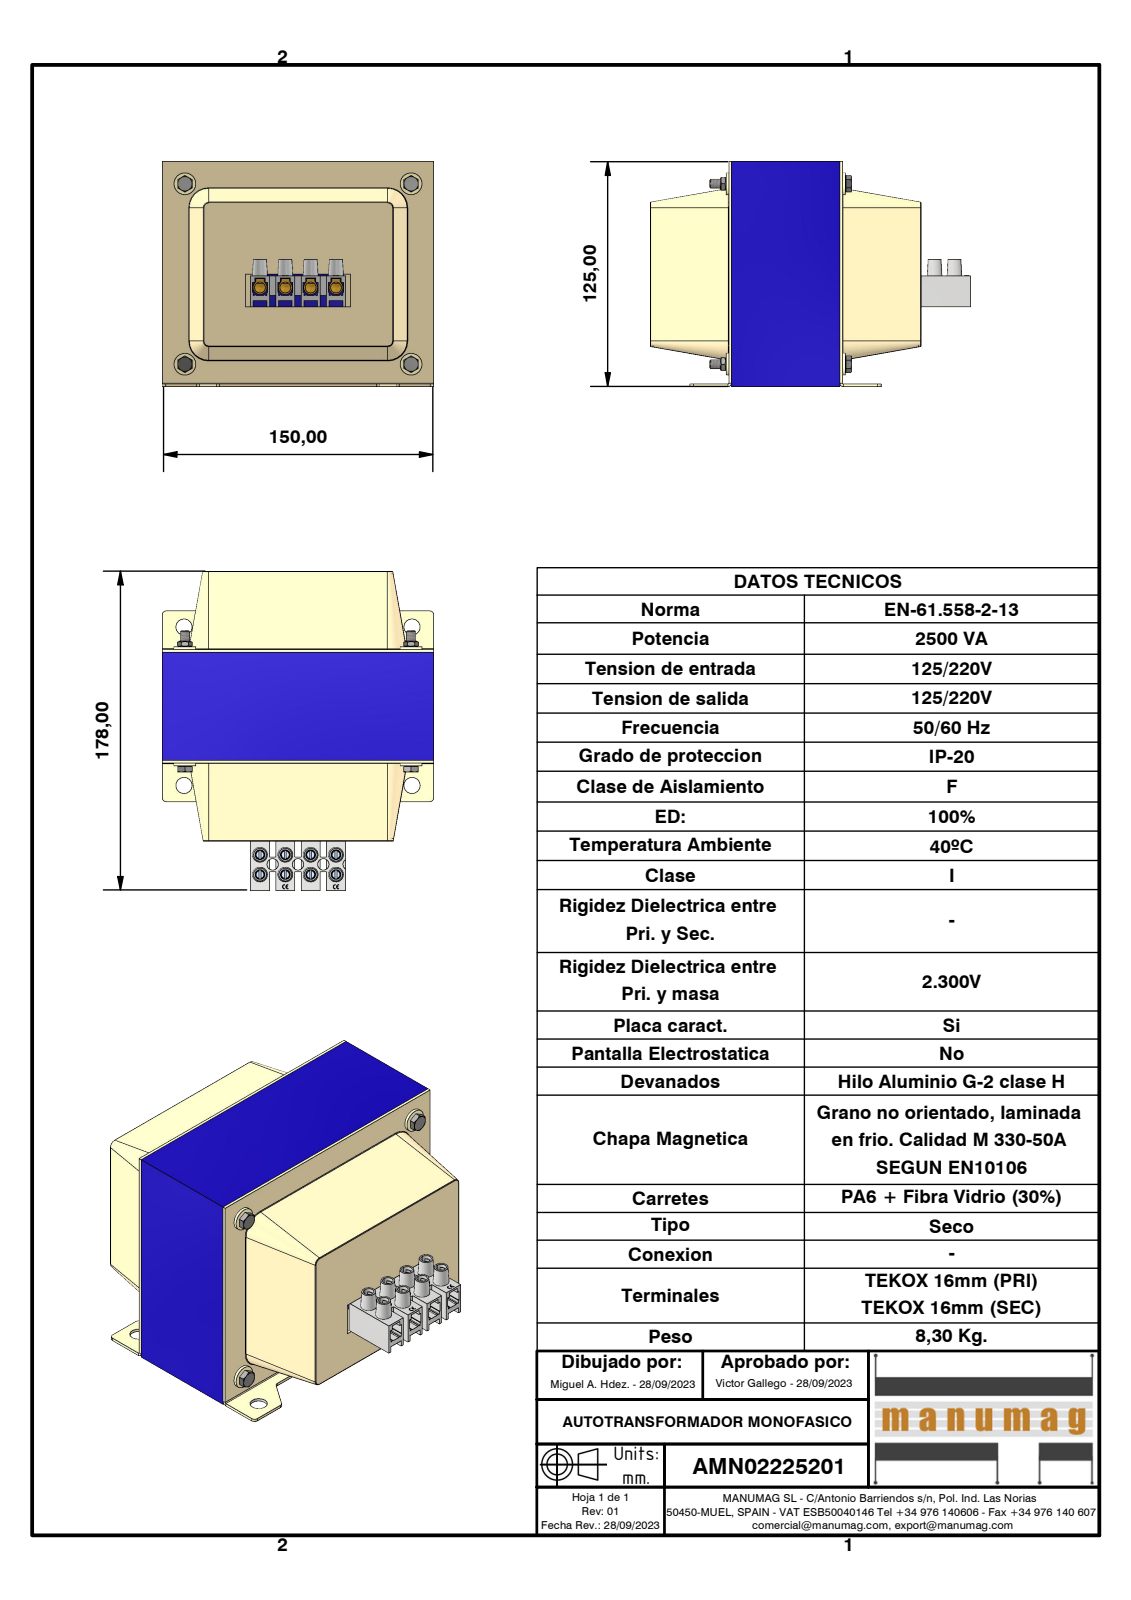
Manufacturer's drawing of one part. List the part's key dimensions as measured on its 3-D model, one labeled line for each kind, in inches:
Part name (STEP PRODUCT): AMN02225201; EI150 x 125 - 60 (RC50) Azul; TAPA RC50 CIEGA; TAPA RC50 VENTANA 4 ELEMENTOS 16 (+8 more)
STEP written by: Autodesk Inventor 2023 (AUTOMOTIVE_DESIGN)
Units: inches
Bodies: 40 solids, 1657 faces (1104 planar, 226 cylindrical, 327 other)
Overall size (bounding box): 6.988 × 5.906 × 4.921
Volume: 59.08 in³ · Surface area: 404.3 in²
Round holes (diameter × count): ⌀0.128 ×12, ⌀0.217 ×8, ⌀0.236 ×8, ⌀0.197 ×4, ⌀0.315 ×4, ⌀0.354 ×4, ⌀0.248 ×3
Round bosses / shafts (diameter × count): ⌀0.157 ×8, ⌀0.472 ×4, ⌀0.264 ×4, ⌀0.232 ×4, ⌀0.18 ×4
Partial cylindrical surfaces — rounded edges, fillets, slot ends (radius × count): R0.015 ×16, R0.108 ×16, R0.079 ×14, R0.032 ×8, R0.118 ×8, R0.009 ×6, R0.004 ×4, R0.032 ×4
Main face-to-face distances: 0.059, 1.713, 4.134, 0.984, 2.362, 3.937, 4.921, 4.12, 1.654, 4.075
Hole centre spacings: 0.551, 1.102, 0.346, 0.354, 0.701, 0.433, 0.853, 0.856
